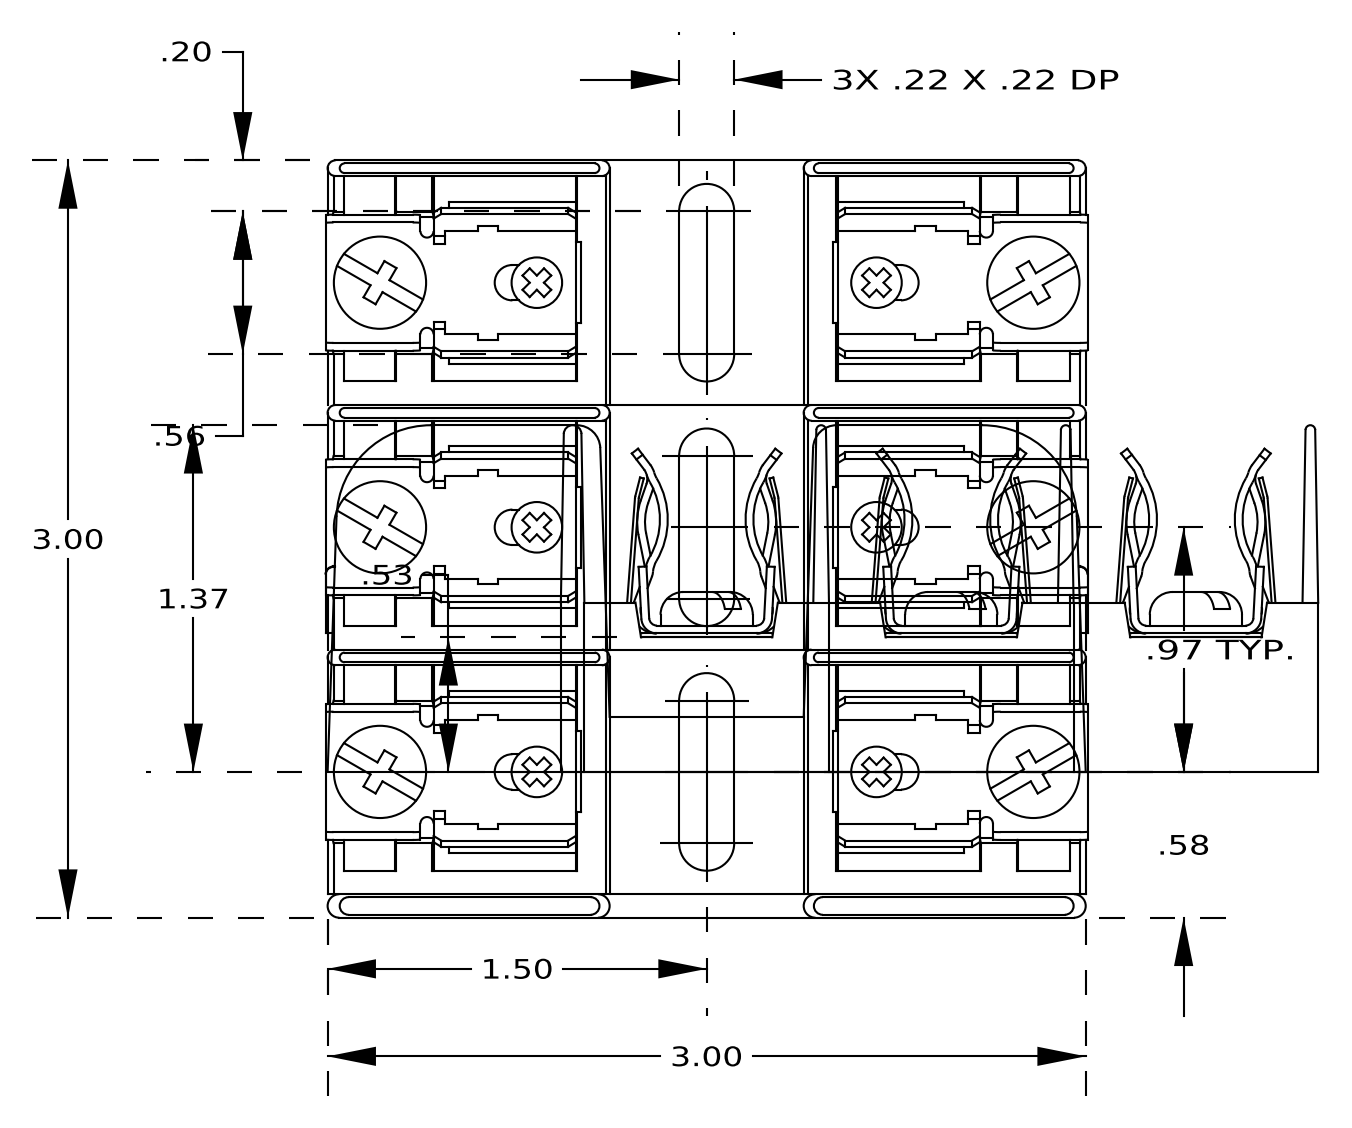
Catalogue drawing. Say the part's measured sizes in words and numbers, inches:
The part is named "700288rev-_1_13; 700288rev; 700288rev-_1_28; 700288rev-_1_10 (+8 more)". Its 3-D file was written by "SolidWorks 2013 (AUTOMOTIVE_DESIGN)". It is 0 solids with 2342 faces: 1403 planar, 500 cylindrical and 439 other. Overall it measures 3.005 by 3.001 by 1.372 inches. Round holes: 6 of diameter 0.159. Round bosses or shafts: 6 of diameter 0.374, 6 of diameter 0.239, 6 of diameter 0.19, 6 of diameter 0.138, 6 of diameter 0.101, 6 of diameter 0.084, 4 of diameter 0.235, 2 of diameter 0.235. Partial cylindrical surfaces (rounded edges, fillets, slot ends): 62 of radius 0.031, 32 of radius 0.01, 30 of radius 0.05, 24 of radius 0.03, 12 of radius 0.065, 12 of radius 0.07, 12 of radius 0.151, 10 of radius 0.093. The main face-to-face distances are 0.97, 0.968, 0.015, 0.533, 0.046, 0.031, 0.093, 1.94, 1.063, 1.938. The hole center spacings are 0.97, 2.752, 2.575, 1.94, 3.224.
